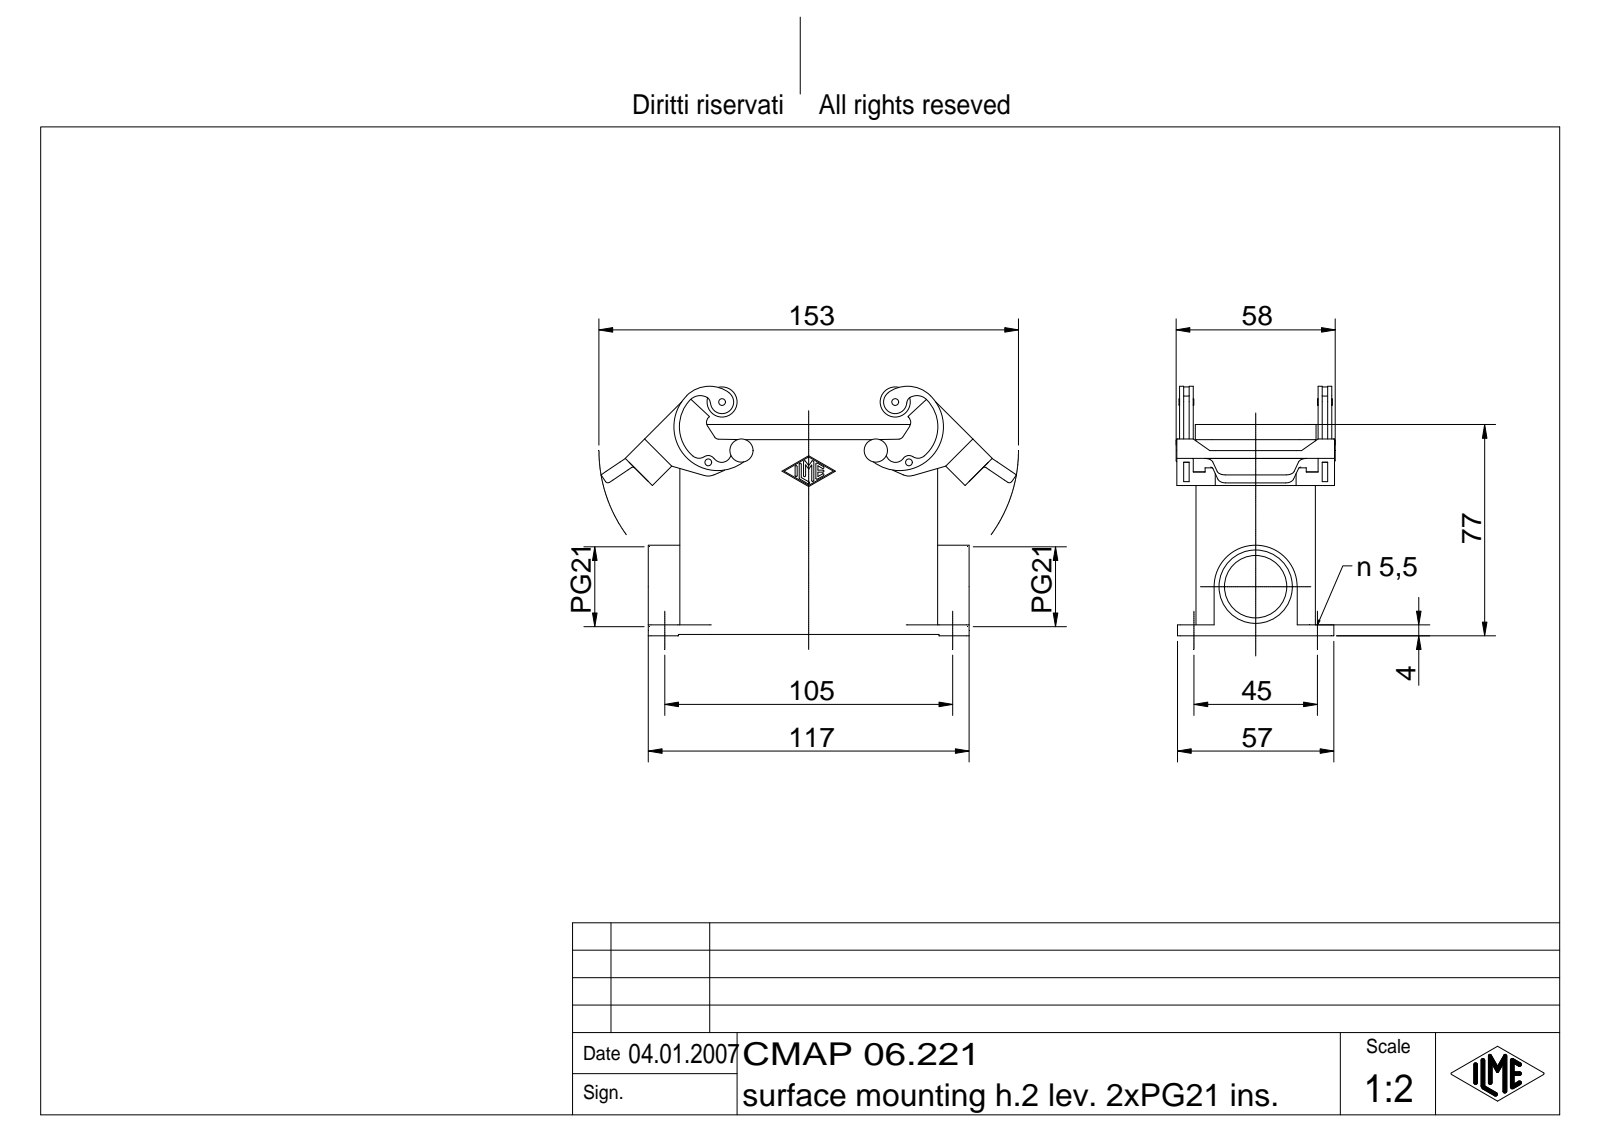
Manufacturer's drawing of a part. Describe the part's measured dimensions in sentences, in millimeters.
The part is named "CMAP 06.221". Its 3-D file was written by "Autodesk Inventor 7 (AUTOMOTIVE_DESIGN)". It is 1 solid with 748 faces: 191 planar, 205 cylindrical and 352 other. Overall it measures 151.49 by 90.94 by 58 millimeters. Its volume is 123 974 cubic millimeters and its surface area 68 451 square millimeters. Round holes: 4 of diameter 2, 4 of diameter 5.5, 2 of diameter 2.5, 1 of diameter 22.78, 1 of diameter 26.78. Round bosses or shafts: 2 of diameter 11, 2 of diameter 5, 2 of diameter 3. Partial cylindrical surfaces (rounded edges, fillets, slot ends): 20 of radius 1, 14 of radius 0.38, 12 of radius 3, 8 of radius 6, 6 of radius 2.5, 4 of radius 1.5, 4 of radius 2, 4 of radius 3.5. The main face-to-face distances are 3, 40.5, 43.5, 37.5, 3.5, 4, 0.75, 50.5, 11, 40.75. The hole center spacings are 22.56, 45, 71.62, 105, 114.24, 63.14, 73.18.
